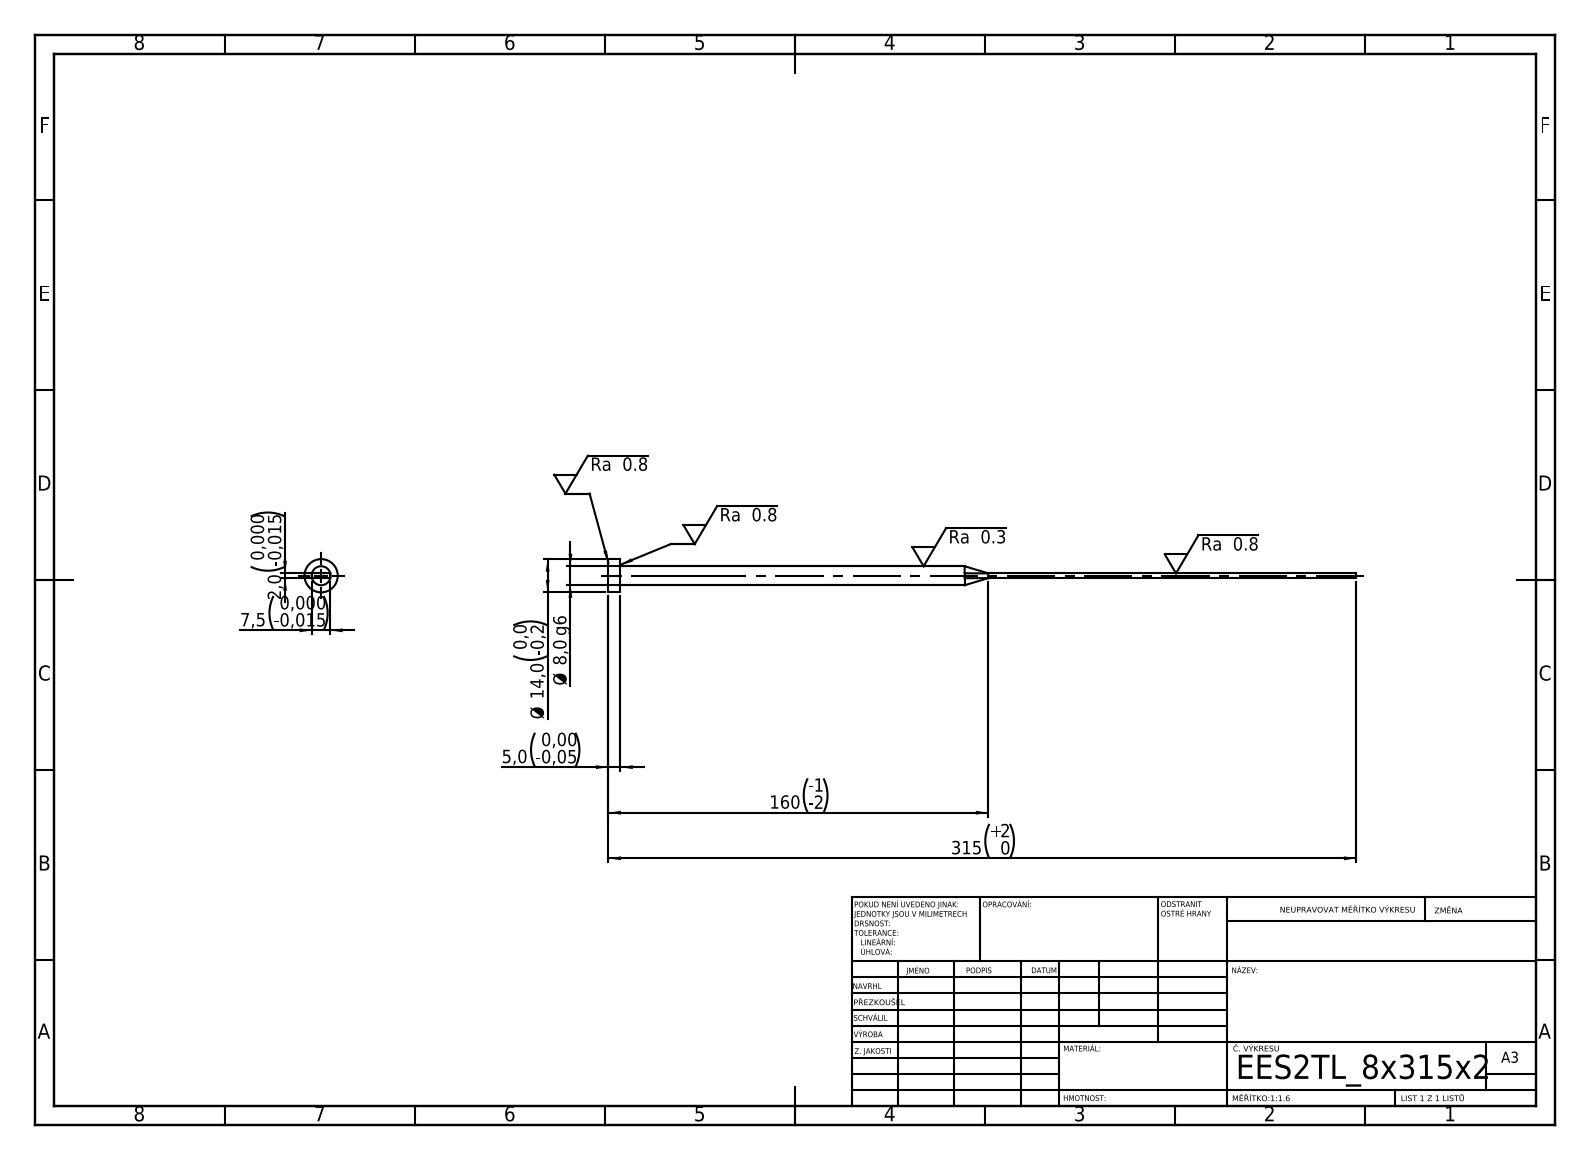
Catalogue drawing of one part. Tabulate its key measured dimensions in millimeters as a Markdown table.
| quantity | value |
| --- | --- |
| STEP written by | SolidWorks 2019 (CONFIG_CONTROL_DESIGN) |
| units | millimeters |
| bodies | 1 solid, 15 faces (7 planar, 4 cylindrical, 4 other) |
| overall size | 315 × 14 × 14 |
| volume | 10 698 mm³ |
| surface area | 7 298 mm² |
| round bosses / shafts (diameter × count) | 14 × 1, 8 × 1 |
| main face-to-face distances | 2, 7.5, 5, 315, 310 |
